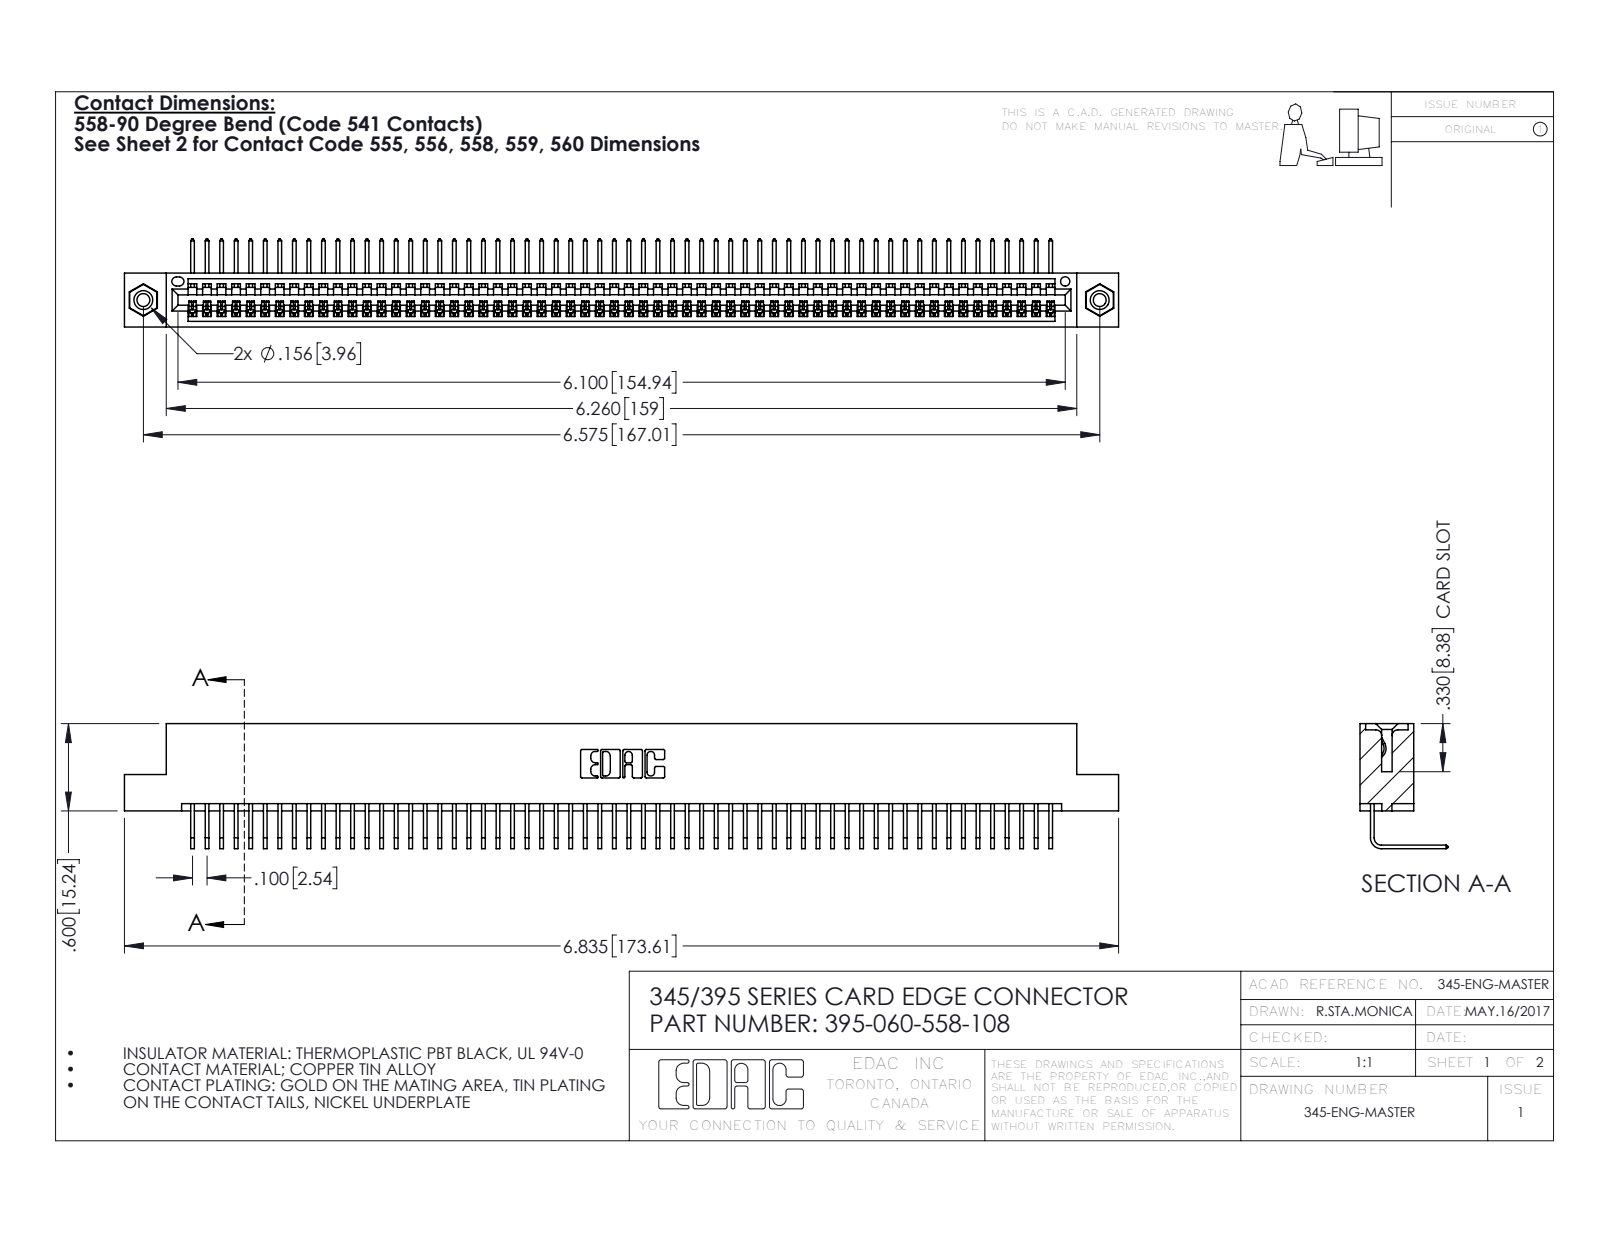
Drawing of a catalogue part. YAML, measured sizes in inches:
part_name: "395-060-558-108; 345 Part_Flush Mounting Lugs - 0.156 Dia-TI; 345-292-001_558 Tail - 2; 345-250-001_345-250-003-102"
step_written_by: "SolidWorks 2016 (CONFIG_CONTROL_DESIGN)"
units: inches
bodies: {solids: 63, faces: 3786, planar: 2632, cylindrical: 1138, other: 16}
overall_size: [6.835, 0.859, 0.605]
volume: 1.027
surface_area: 36.9
round_holes:
  - {diameter: 0.089, count: 2}
  - {diameter: 0.125, count: 2}
  - {diameter: 0.156, count: 2}
  - {diameter: 0.064, count: 1}
round_bosses_or_shafts:
  - {diameter: 0.155, count: 2}
partial_cylinders:
  - {radius: 0.006, count: 120}
  - {radius: 0.01, count: 22}
  - {radius: 0.007, count: 6}
  - {radius: 0.031, count: 6}
  - {radius: 0.026, count: 3}
  - {radius: 0.031, count: 2}
  - {radius: 0.04, count: 2}
  - {radius: 0.014, count: 1}
face_to_face_distances: [0.072, 0.298, 0.37, 0.2, 0.098, 0.272, 0.025, 0.225, 0.149, 0.072]
hole_center_spacings: [0.27, 6.339, 6.575]
